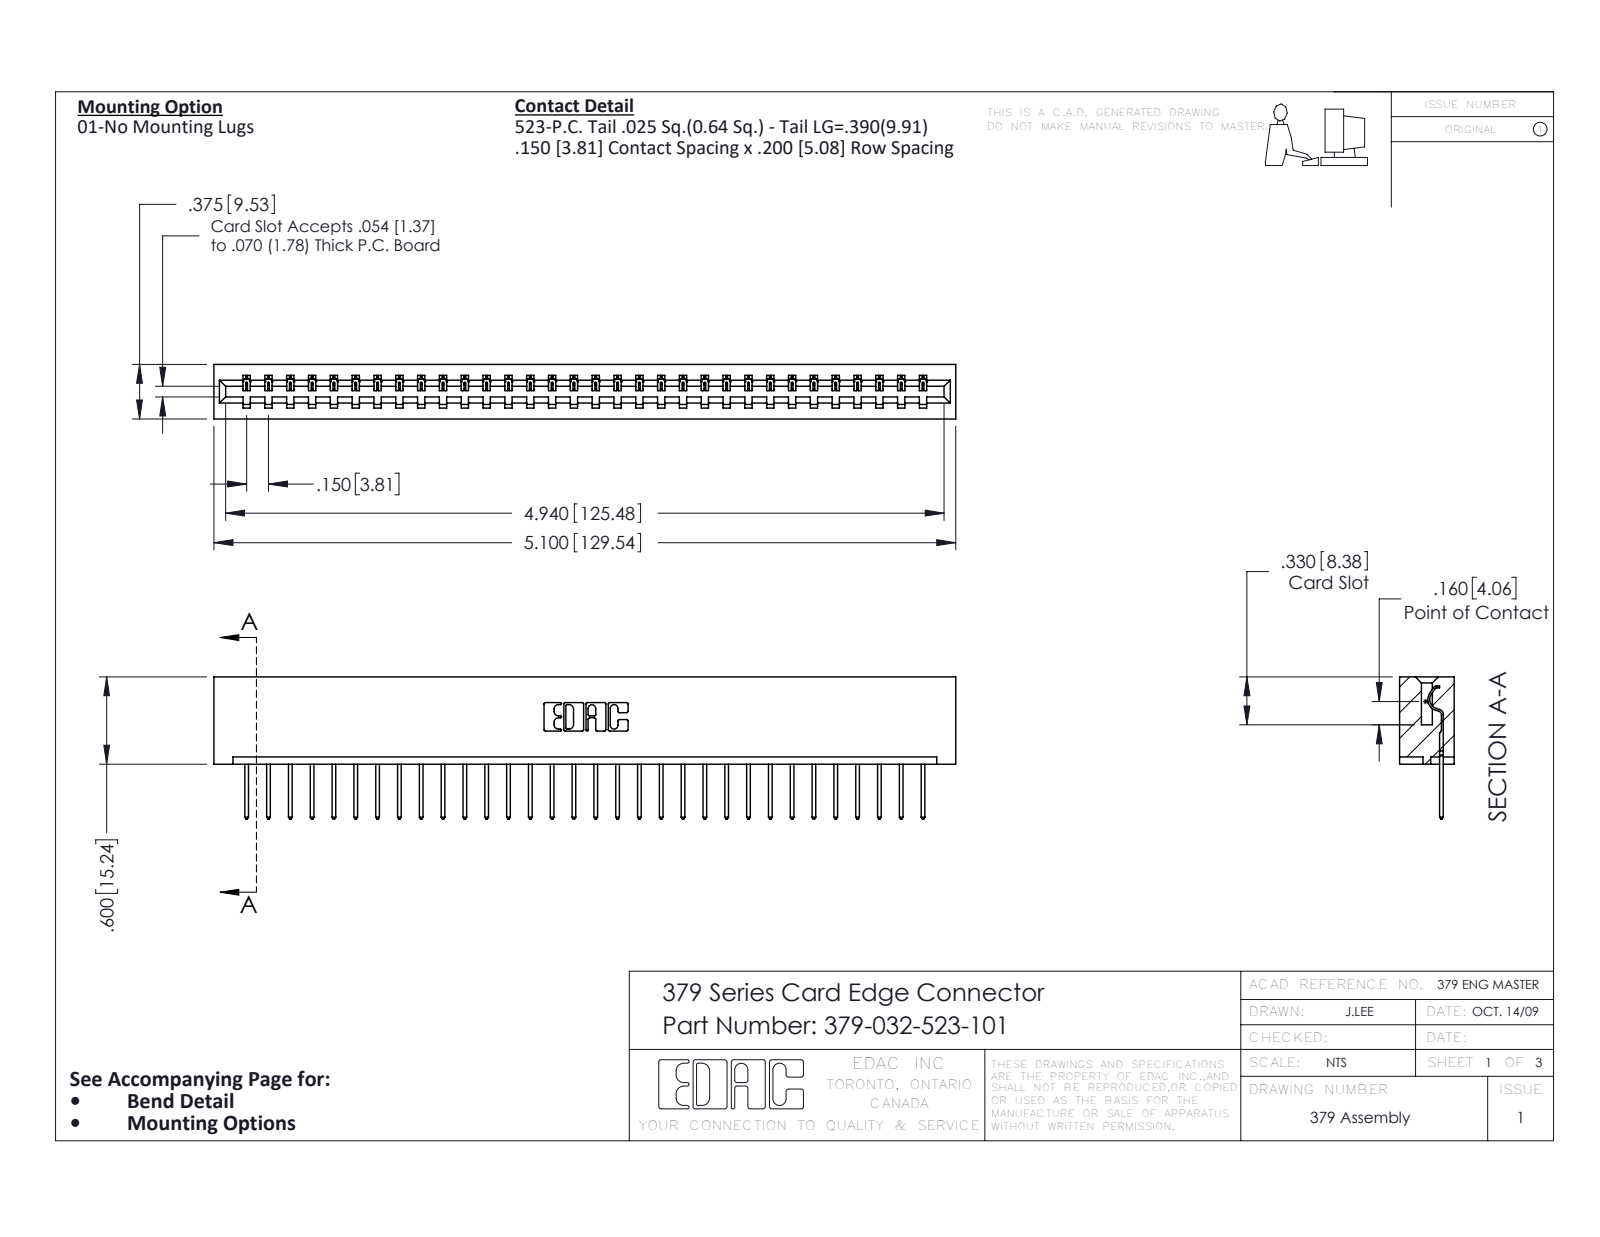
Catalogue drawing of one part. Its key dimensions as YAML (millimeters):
part_name: "345-292-001_345-293-123; 379-032-523-101; 379 Part_Lugless"
step_written_by: "SolidWorks 2016 (CONFIG_CONTROL_DESIGN)"
units: millimeters
bodies: {solids: 33, faces: 1962, planar: 1410, cylindrical: 552, other: 0}
overall_size: [129.5, 24.8, 9.5]
volume: 14200
surface_area: 14470
partial_cylinders:
  - {radius: 0.2, count: 64}
  - {radius: 0.3, count: 64}
  - {radius: 0.3, count: 22}
  - {radius: 0.2, count: 6}
  - {radius: 0.8, count: 6}
  - {radius: 0.7, count: 3}
  - {radius: 0.4, count: 1}
  - {radius: 0.6, count: 1}
face_to_face_distances: [7.6, 1.9, 9.5, 5.7, 15.2, 2.5, 7, 0.6, 5.1, 3.8]
